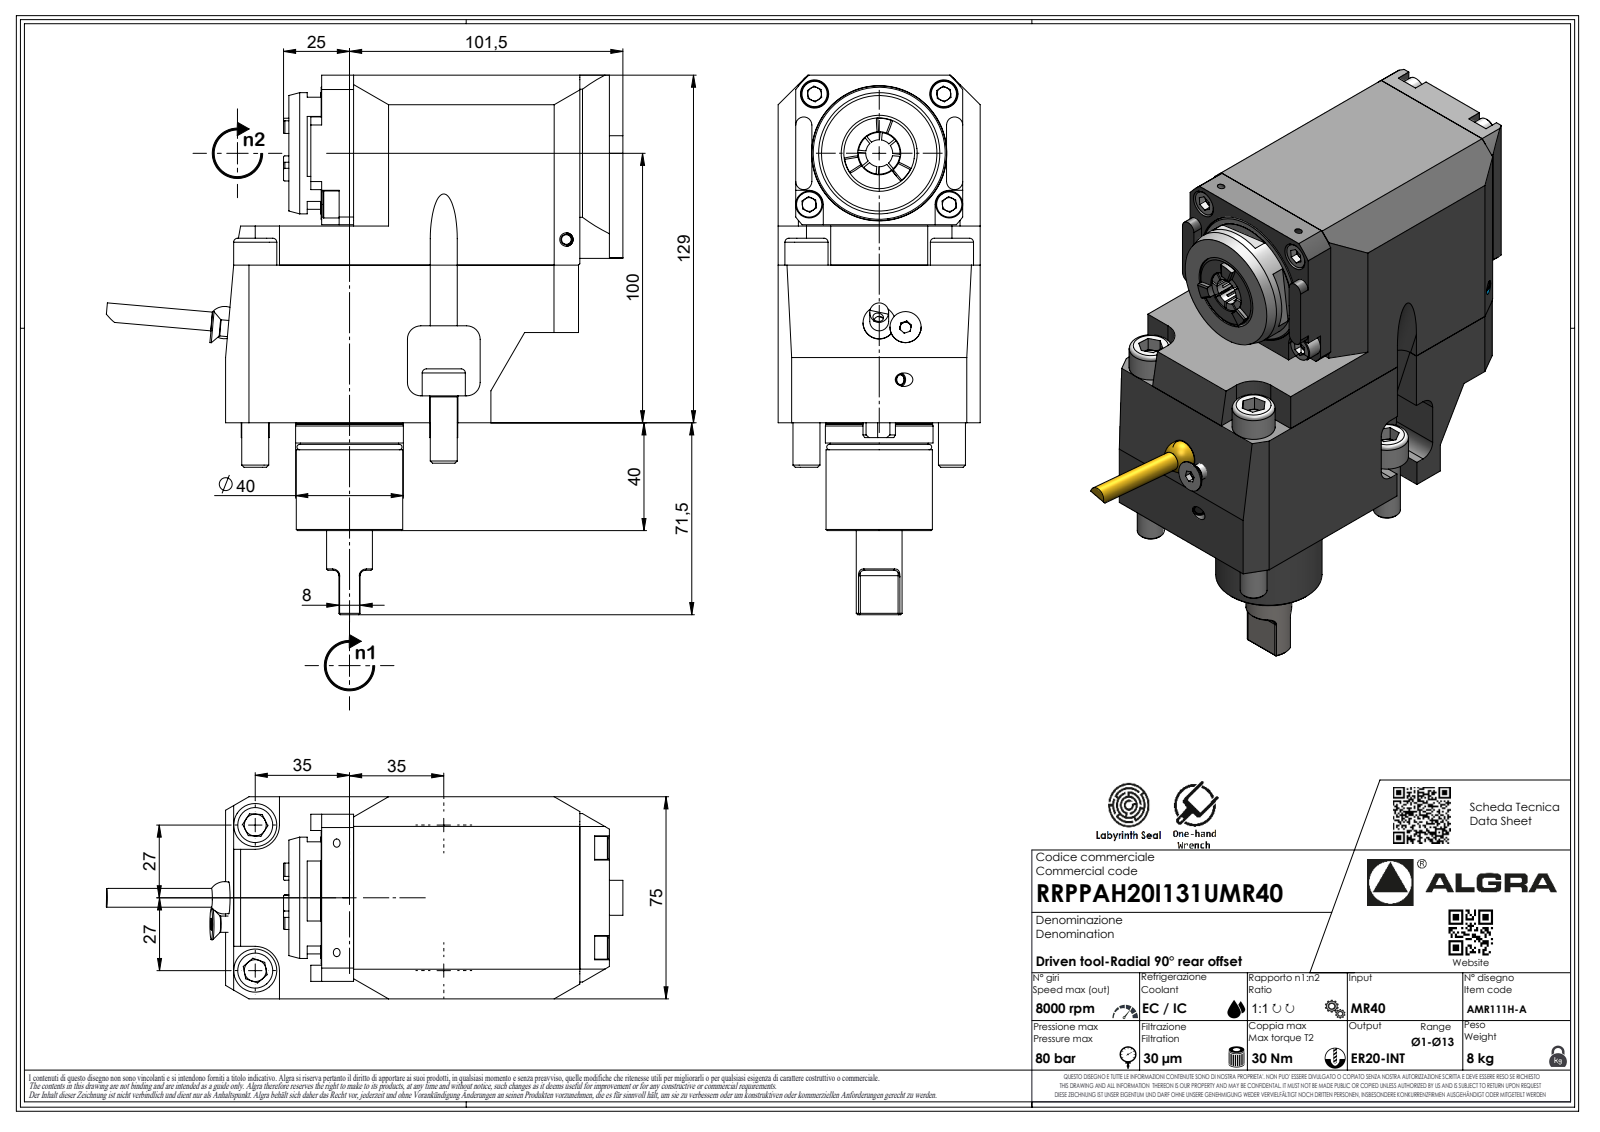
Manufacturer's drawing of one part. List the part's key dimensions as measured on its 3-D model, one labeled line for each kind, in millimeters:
Part name (STEP PRODUCT): RRPPAH20I131UMR40
STEP written by: SolidWorks 2023 (AUTOMOTIVE_DESIGN)
Units: millimetres
Bodies: 1 solid, 545 faces (358 planar, 81 cylindrical, 106 other)
Overall size (bounding box): 200.2 × 191.77 × 75
Volume: 1 131 000 mm³ · Surface area: 83 066 mm²
Round holes (diameter × count): ⌀2.1 ×1, ⌀4 ×1, ⌀5 ×1, ⌀8.57 ×1, ⌀12 ×1
Round bosses / shafts (diameter × count): ⌀10 ×4, ⌀16 ×2, ⌀45 ×1, ⌀40 ×1, ⌀39.6 ×1, ⌀39.5 ×1, ⌀37.44 ×1, ⌀17 ×1
Partial cylindrical surfaces — rounded edges, fillets, slot ends (radius × count): R0.33 ×7, R0.52 ×7, R2 ×7, R3.7 ×7, R3 ×4, R3.25 ×2, R5.25 ×2, R6 ×2
Main face-to-face distances: 75, 129, 56, 73, 68.5, 11.5, 95.5, 73.5, 23.5, 40
